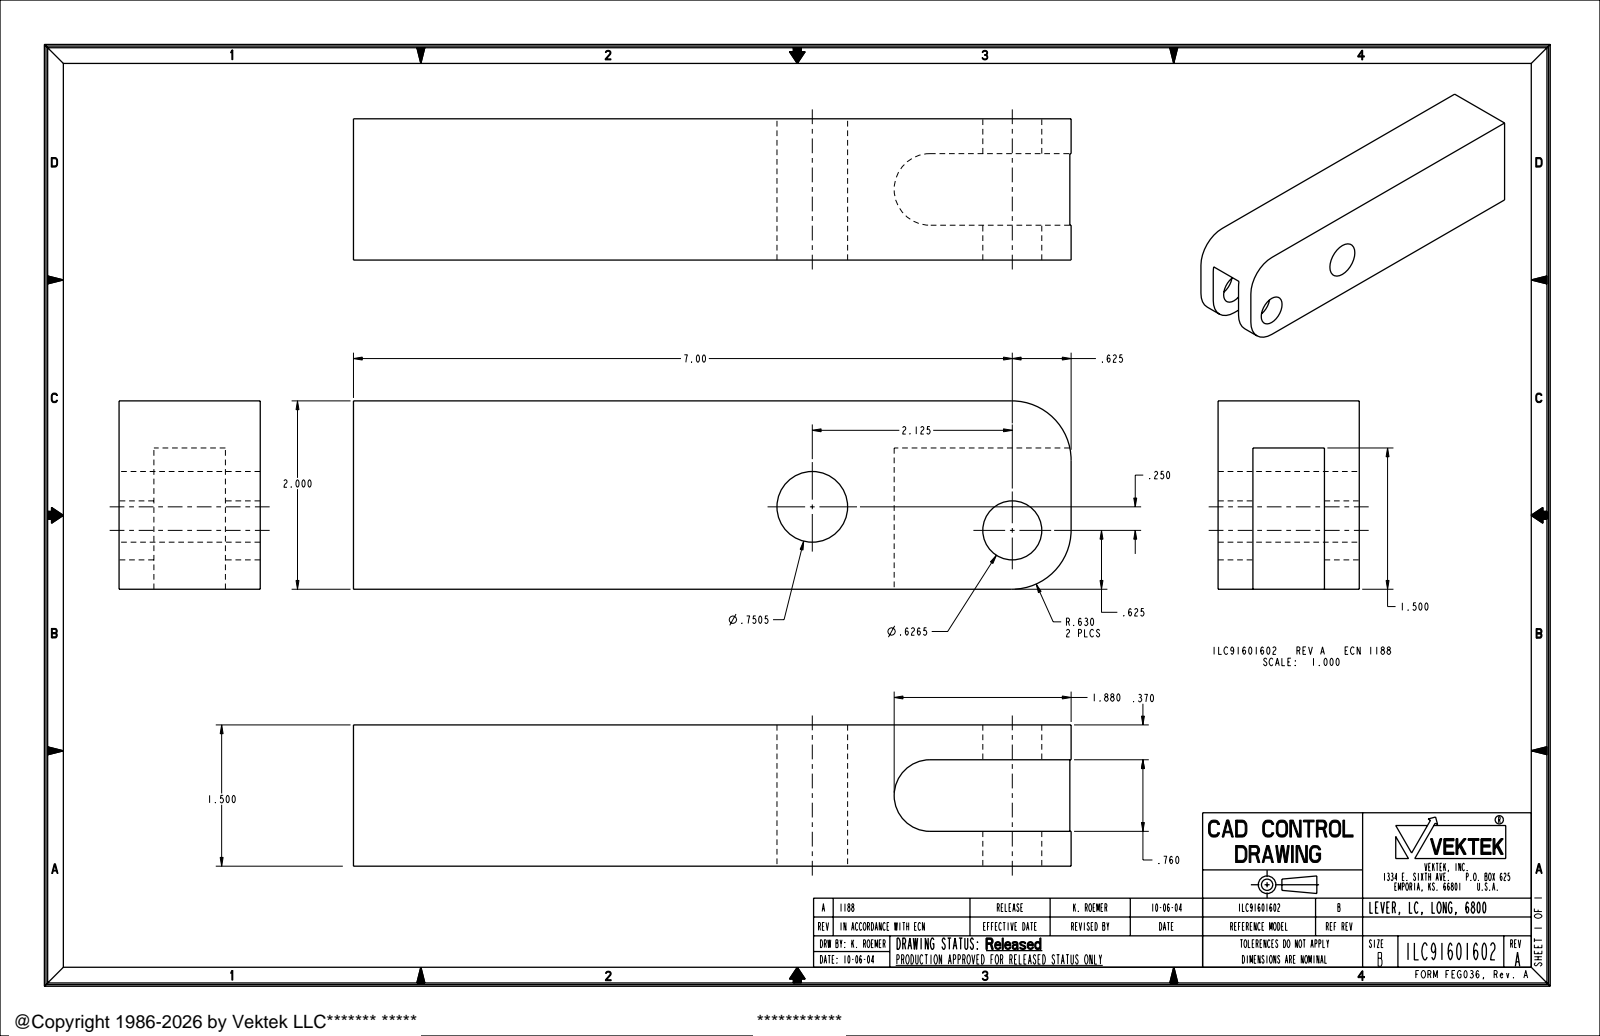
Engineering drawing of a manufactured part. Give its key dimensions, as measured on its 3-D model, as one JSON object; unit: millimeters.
{"part_name": "91601602", "step_written_by": "PRO/ENGINEER BY PARAMETRIC TECHNOLOGY CORPORATION, 2004290 (CONFIG_CONTROL_DESIGN)", "units": "millimeters", "bodies": {"solids": 1, "faces": 20, "planar": 10, "cylindrical": 10, "other": 0}, "overall_size": [193.7, 50.8, 38.1], "volume_mm3": 323500, "surface_area_mm2": 42750, "round_holes": [[15.9, 1], [19.1, 1]], "partial_cylinders_radius": [[16, 2], [9.7, 1]], "face_to_face_distances": [38.1, 50.8, 9.4, 28.7, 19.3, 12.7, 193.7], "hole_center_spacings": [54.3]}
